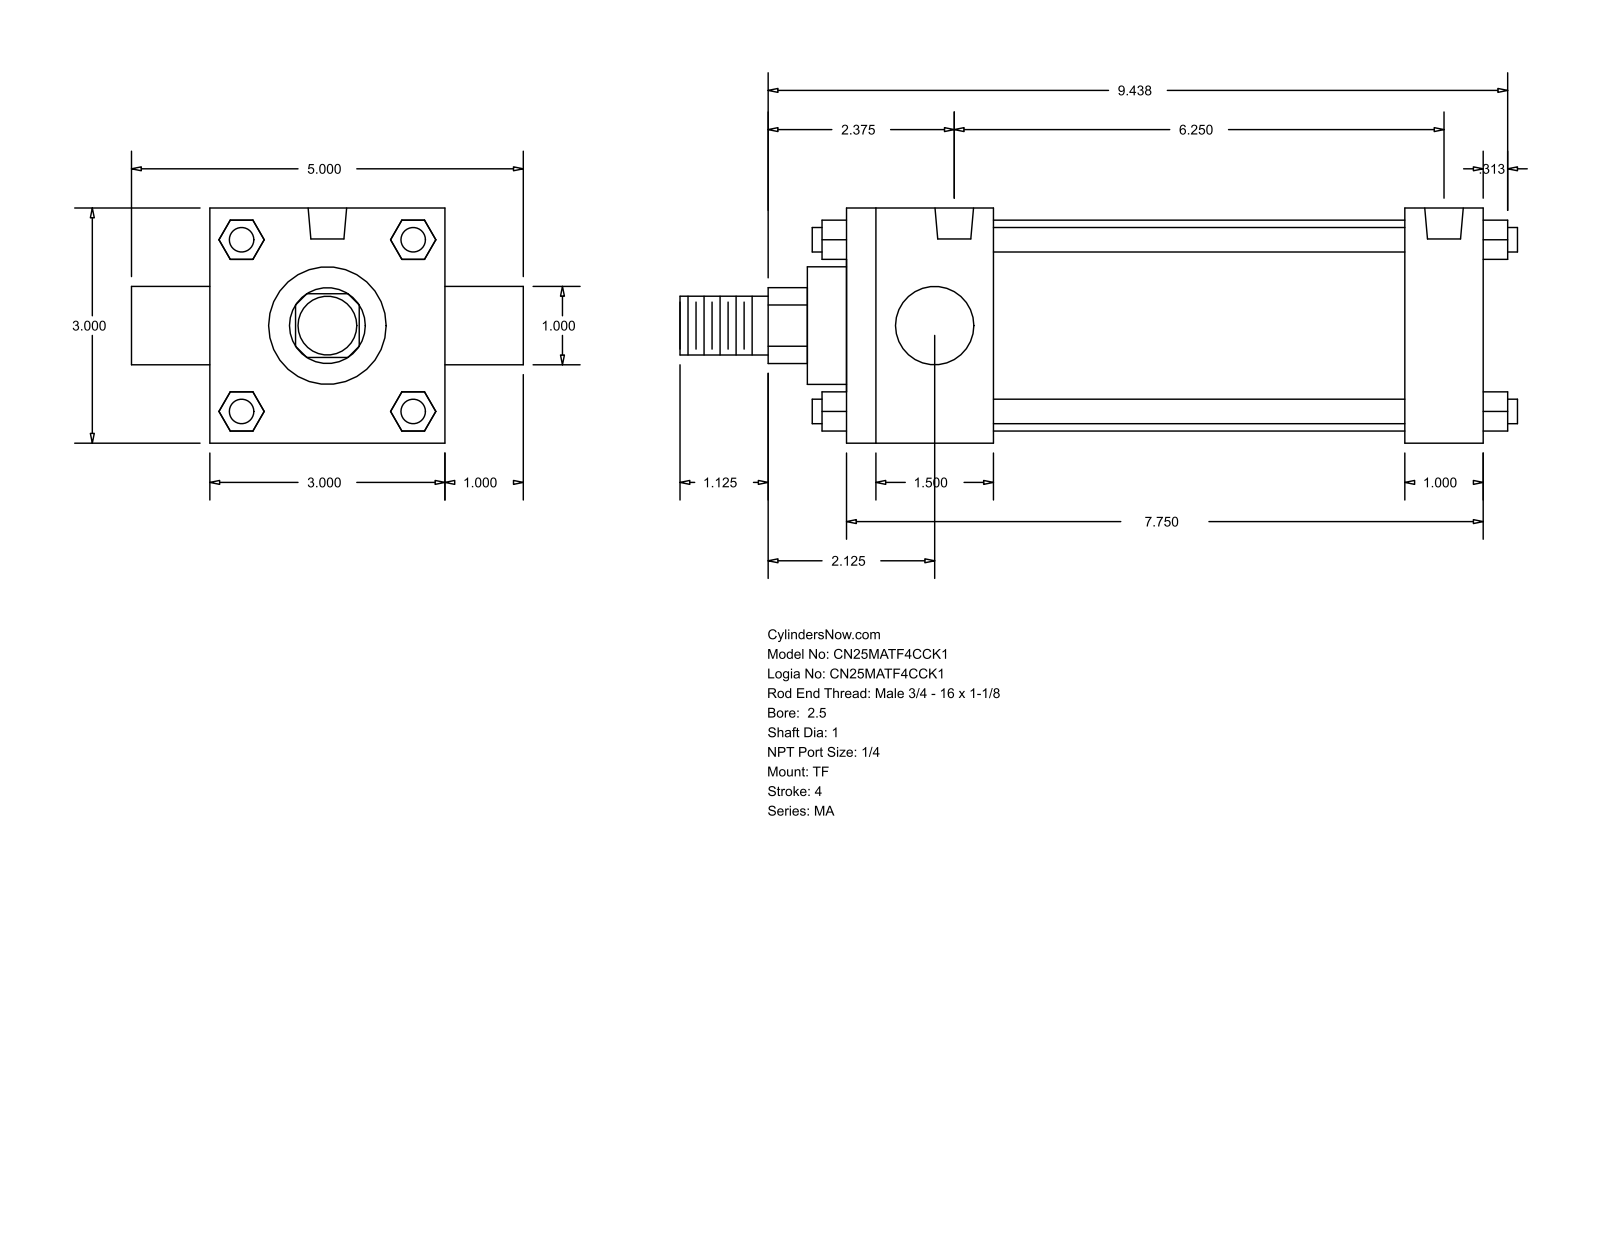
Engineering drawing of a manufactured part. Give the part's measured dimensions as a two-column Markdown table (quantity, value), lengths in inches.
| quantity | value |
| --- | --- |
| part name | MA_TF__0250_1 |
| STEP written by | GSSL Pune (CONFIG_CONTROL_DESIGN) |
| units | inches |
| bodies | 0 solids, 120 faces (92 planar, 28 cylindrical, 0 other) |
| overall size | 10.687 × 5 × 3 |
| round holes (diameter × count) | 0.313 × 3, 0.492 × 2 |
| round bosses / shafts (diameter × count) | 0.313 × 4, 1 × 2, 2.69 × 1, 1.5 × 1, 0.75 × 1 |
| partial cylindrical surfaces (radius × count) | 0.484 × 1 |
| main face-to-face distances | 3, 8.125, 1, 0.5, 1.875, 7.125, 5.25, 6.25, 4, 1.095 |
| hole center spacings | 6.25 |
